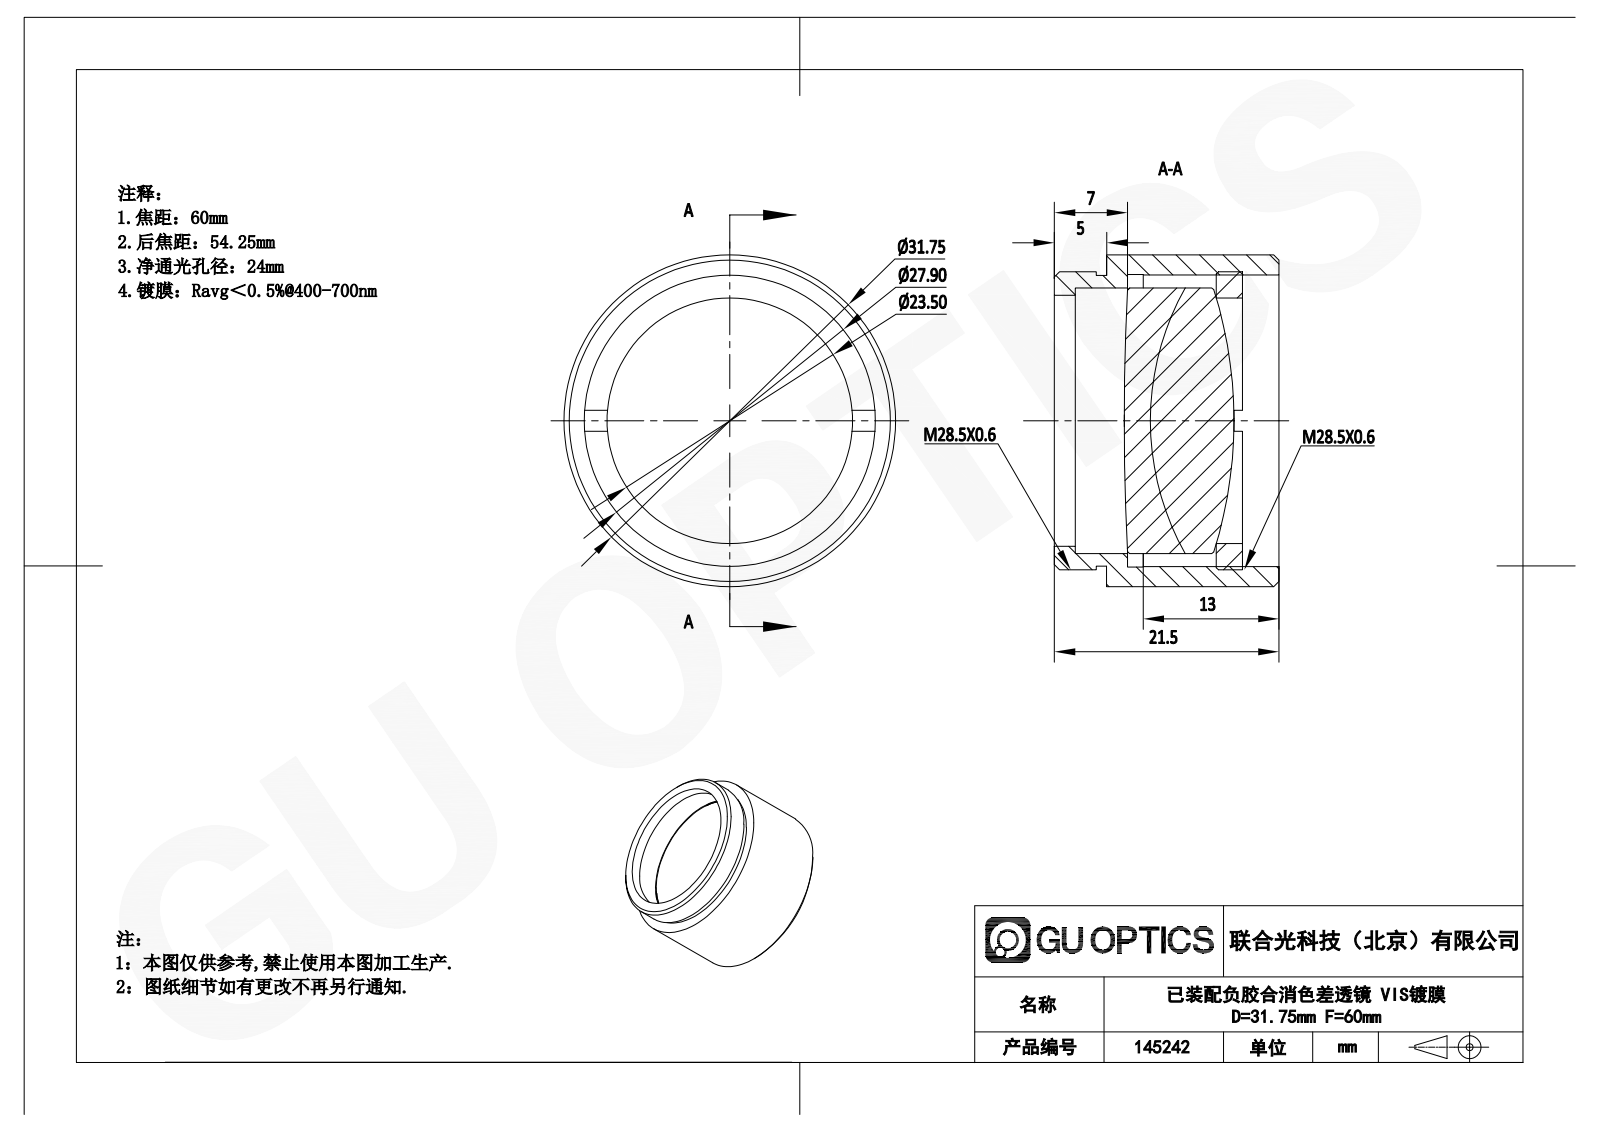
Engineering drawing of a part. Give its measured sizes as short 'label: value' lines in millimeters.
name: APD-ML25-060-VIS; M28.5x0.6ѹȦ; GL31-025B-060-VIS_Solidworks
written by: SolidWorks 2022 (AUTOMOTIVE_DESIGN)
unit: mm
bodies: 4 solids, 56 faces (16 planar, 22 cylindrical, 18 other)
size: 31.76 × 31.76 × 21.5
volume: 9 137 mm³; area: 8 165 mm²
holes: 1× ⌀23.5, 1× ⌀24, 1× ⌀27.9, 1× ⌀28
bosses: 1× ⌀31.76, 1× ⌀28.5, 1× ⌀27.8, 1× ⌀25.4
face distances: 2, 5, 13, 2.5, 10.5, 15.5, 18, 3.5, 21.5, 16.5
